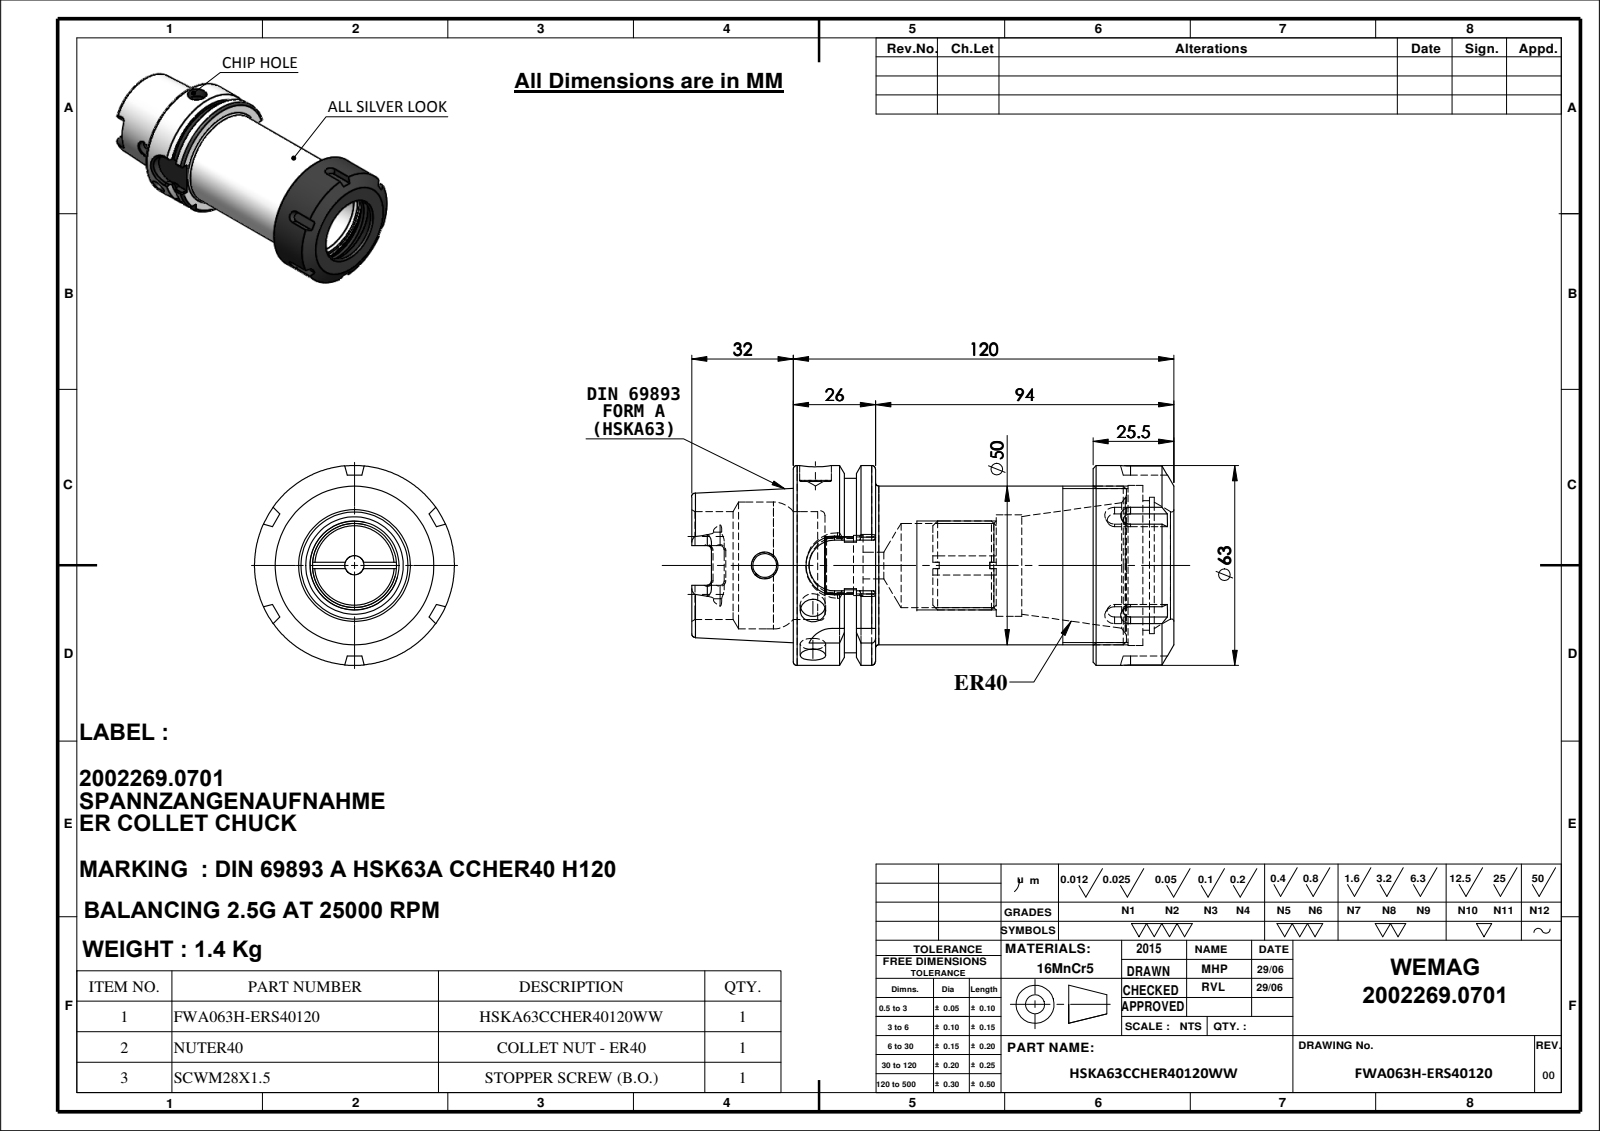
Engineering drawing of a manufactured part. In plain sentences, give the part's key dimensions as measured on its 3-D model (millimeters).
The part is named "SCWM28X1.5; NUTER40; 9163A-ER840120; HSKA63CCHER40120WW". Its 3-D file was written by "SolidWorks 2018 (CONFIG_CONTROL_DESIGN)". It is 3 solids with 249 faces: 92 planar, 65 cylindrical and 92 other. Overall it measures 152 by 63 by 63 millimeters. Its volume is 224 606 cubic millimeters and its surface area 57 579 square millimeters. Round holes: 2 of diameter 8, 1 of diameter 6, 1 of diameter 7.5, 1 of diameter 8.4, 1 of diameter 10, 1 of diameter 17, 1 of diameter 19, 1 of diameter 26.5, 1 of diameter 32, 1 of diameter 34, 1 of diameter 40, 1 of diameter 40.8. Round bosses or shafts: 1 of diameter 63, 1 of diameter 55, 1 of diameter 50, 1 of diameter 28. Partial cylindrical surfaces (rounded edges, fillets, slot ends): 6 of radius 1.3, 4 of radius 2.88, 2 of radius 8, 1 of radius 9. The main face-to-face distances are 120, 25.5, 94.5, 76, 54, 110.2, 15.7, 9.8, 25.95, 68.55. The hole center spacings are 1.9.
